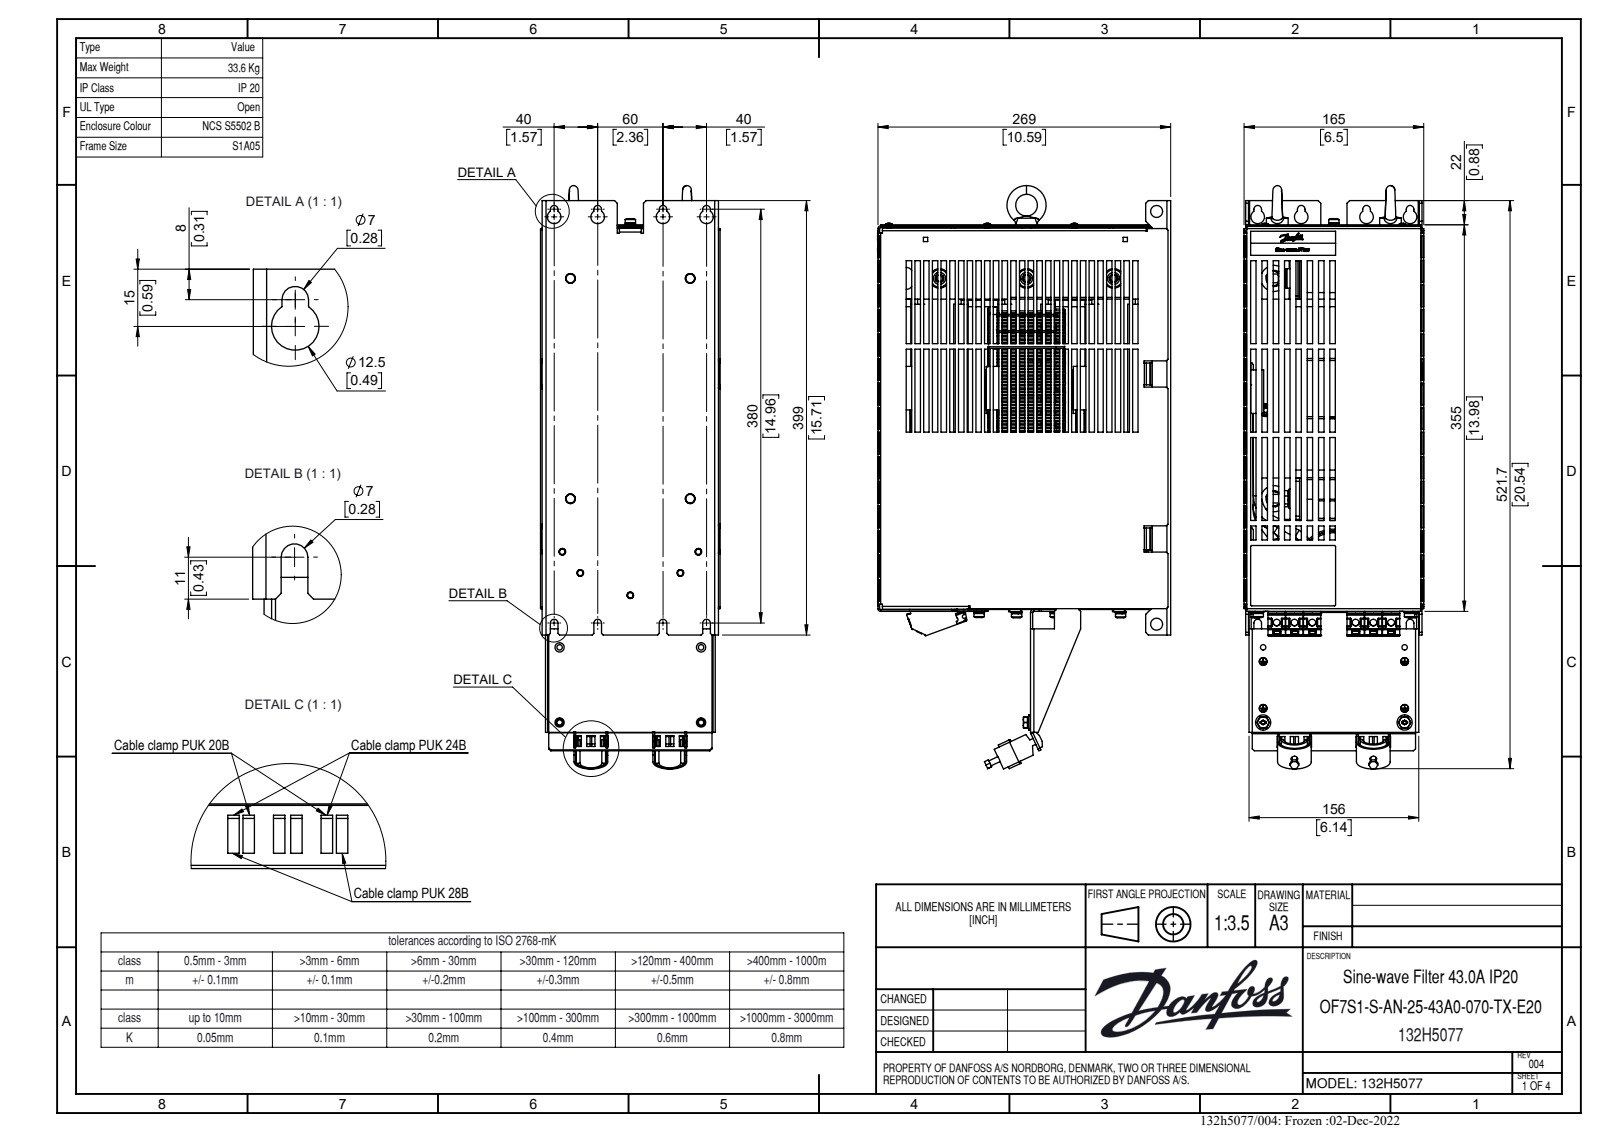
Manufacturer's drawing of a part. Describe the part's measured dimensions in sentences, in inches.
The part is named "PRT0004". Its 3-D file was written by "CREO PARAMETRIC BY PTC INC, 2020342 (CONFIG_CONTROL_DESIGN)". It is 9 solids with 2629 faces: 1896 planar, 471 cylindrical and 262 other. Overall it measures 20.856 by 10.611 by 6.496 inches. Its volume is 865.9 cubic inches and its surface area 1 495 square inches. Round holes: 10 of diameter 0.256, 7 of diameter 0.165, 7 of diameter 0.197, 4 of diameter 0.156, 4 of diameter 0.281, 4 of diameter 0.315, 4 of diameter 0.492, 3 of diameter 0.177, 3 of diameter 0.205, 2 of diameter 0.261, 2 of diameter 0.433. Round bosses or shafts: 8 of diameter 0.315, 8 of diameter 0.276, 4 of diameter 0.35, 4 of diameter 0.26, 4 of diameter 0.197, 4 of diameter 0.157, 3 of diameter 0.386, 3 of diameter 0.374. Partial cylindrical surfaces (rounded edges, fillets, slot ends): 29 of radius 0.039, 20 of radius 0.118, 12 of radius 0.016, 12 of radius 0.028, 11 of radius 0.138, 5 of radius 0.107, 4 of radius 0.094, 4 of radius 0.165. The main face-to-face distances are 0.098, 6.339, 0.059, 6.398, 0.157, 6.24, 0.039, 6.496, 6.437, 6.28. The hole center spacings are 0.642, 1.175, 0.984, 2.854, 3.019, 1.283, 1.617, 2.213.
